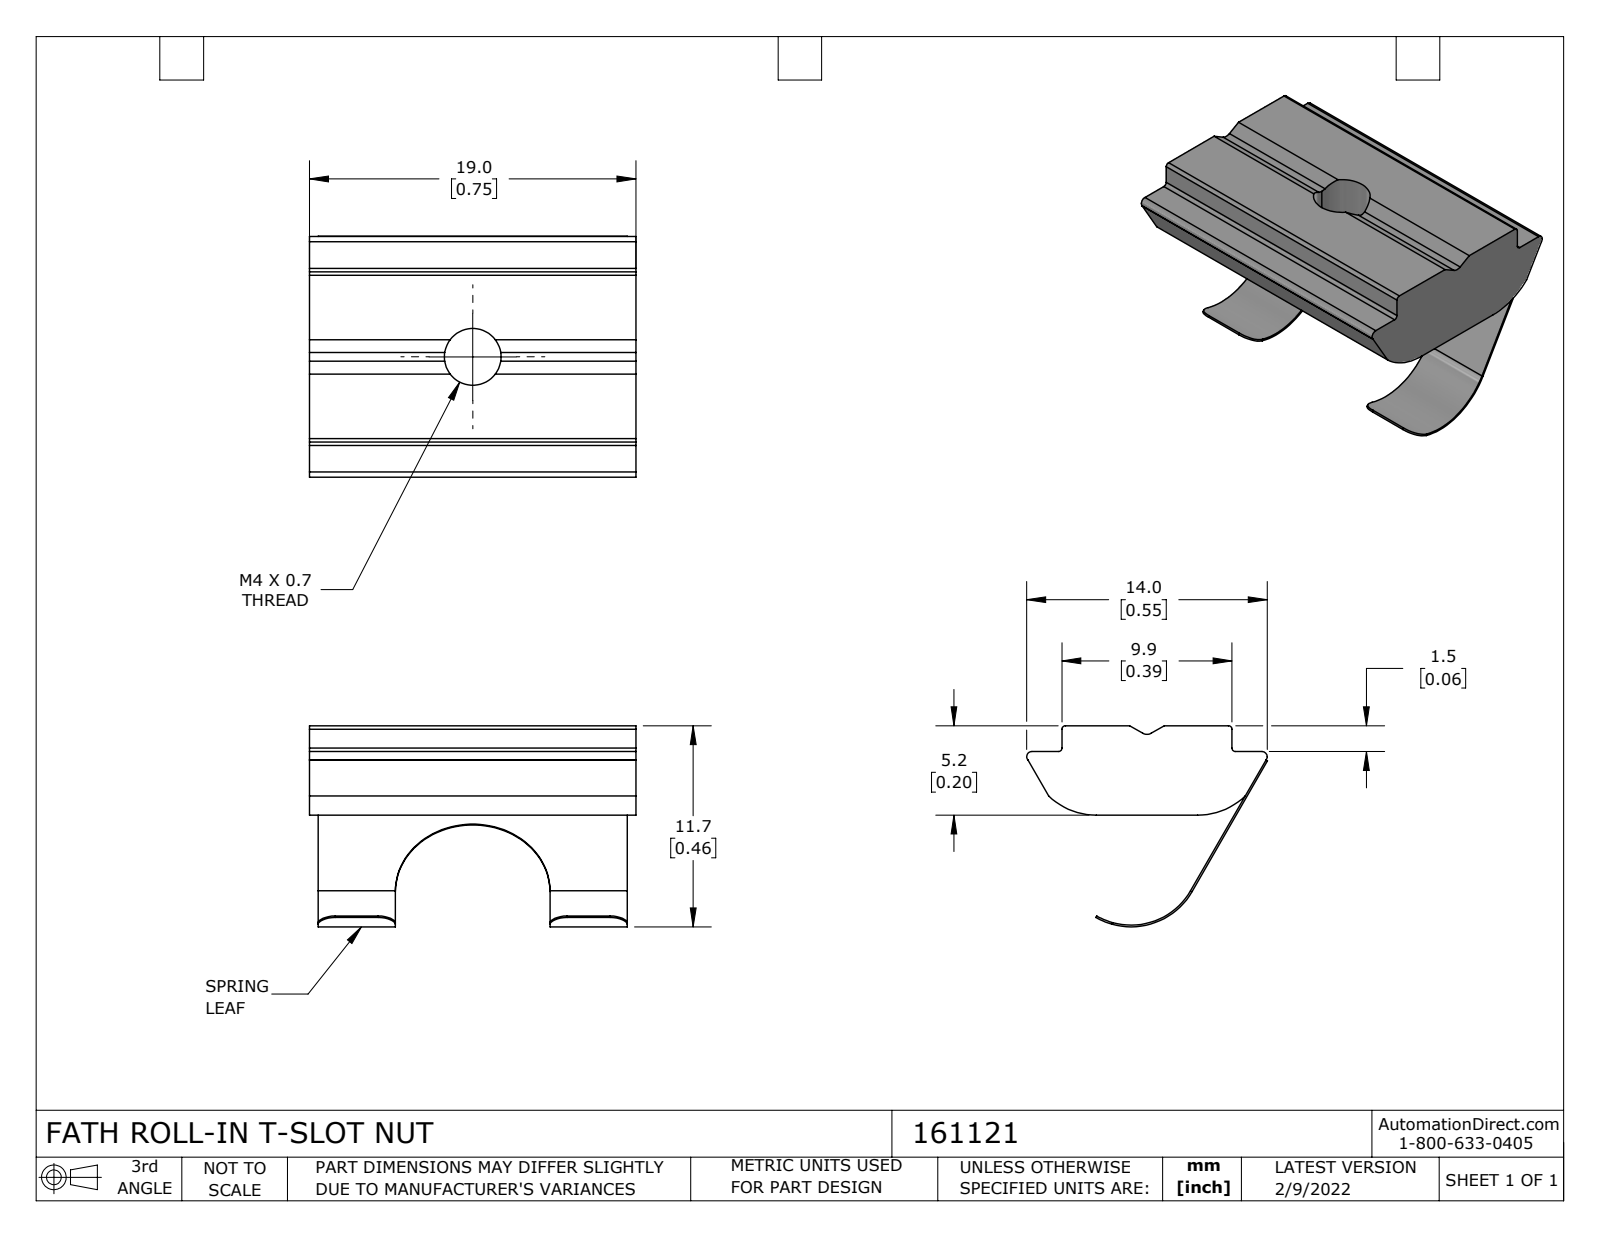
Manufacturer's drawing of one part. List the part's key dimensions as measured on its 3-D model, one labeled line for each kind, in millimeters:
Part name (STEP PRODUCT): 161121
STEP written by: SolidWorks 2021 (CONFIG_CONTROL_DESIGN)
Units: millimetres
Bodies: 1 solid, 48 faces (25 planar, 23 cylindrical, 0 other)
Overall size (bounding box): 19 × 14.02 × 11.7
Volume: 1 086 mm³ · Surface area: 1 095 mm²
Round holes (diameter × count): ⌀3.3 ×1
Partial cylindrical surfaces — rounded edges, fillets, slot ends (radius × count): R0.2 ×4, R1 ×4, R0.3 ×3, R4 ×3, R0.5 ×1, R4.1 ×1, R4.5 ×1
Main face-to-face distances: 5.2, 3.7, 1.5, 19, 9.9, 0.5, 18.5, 2.24, 18, 5
